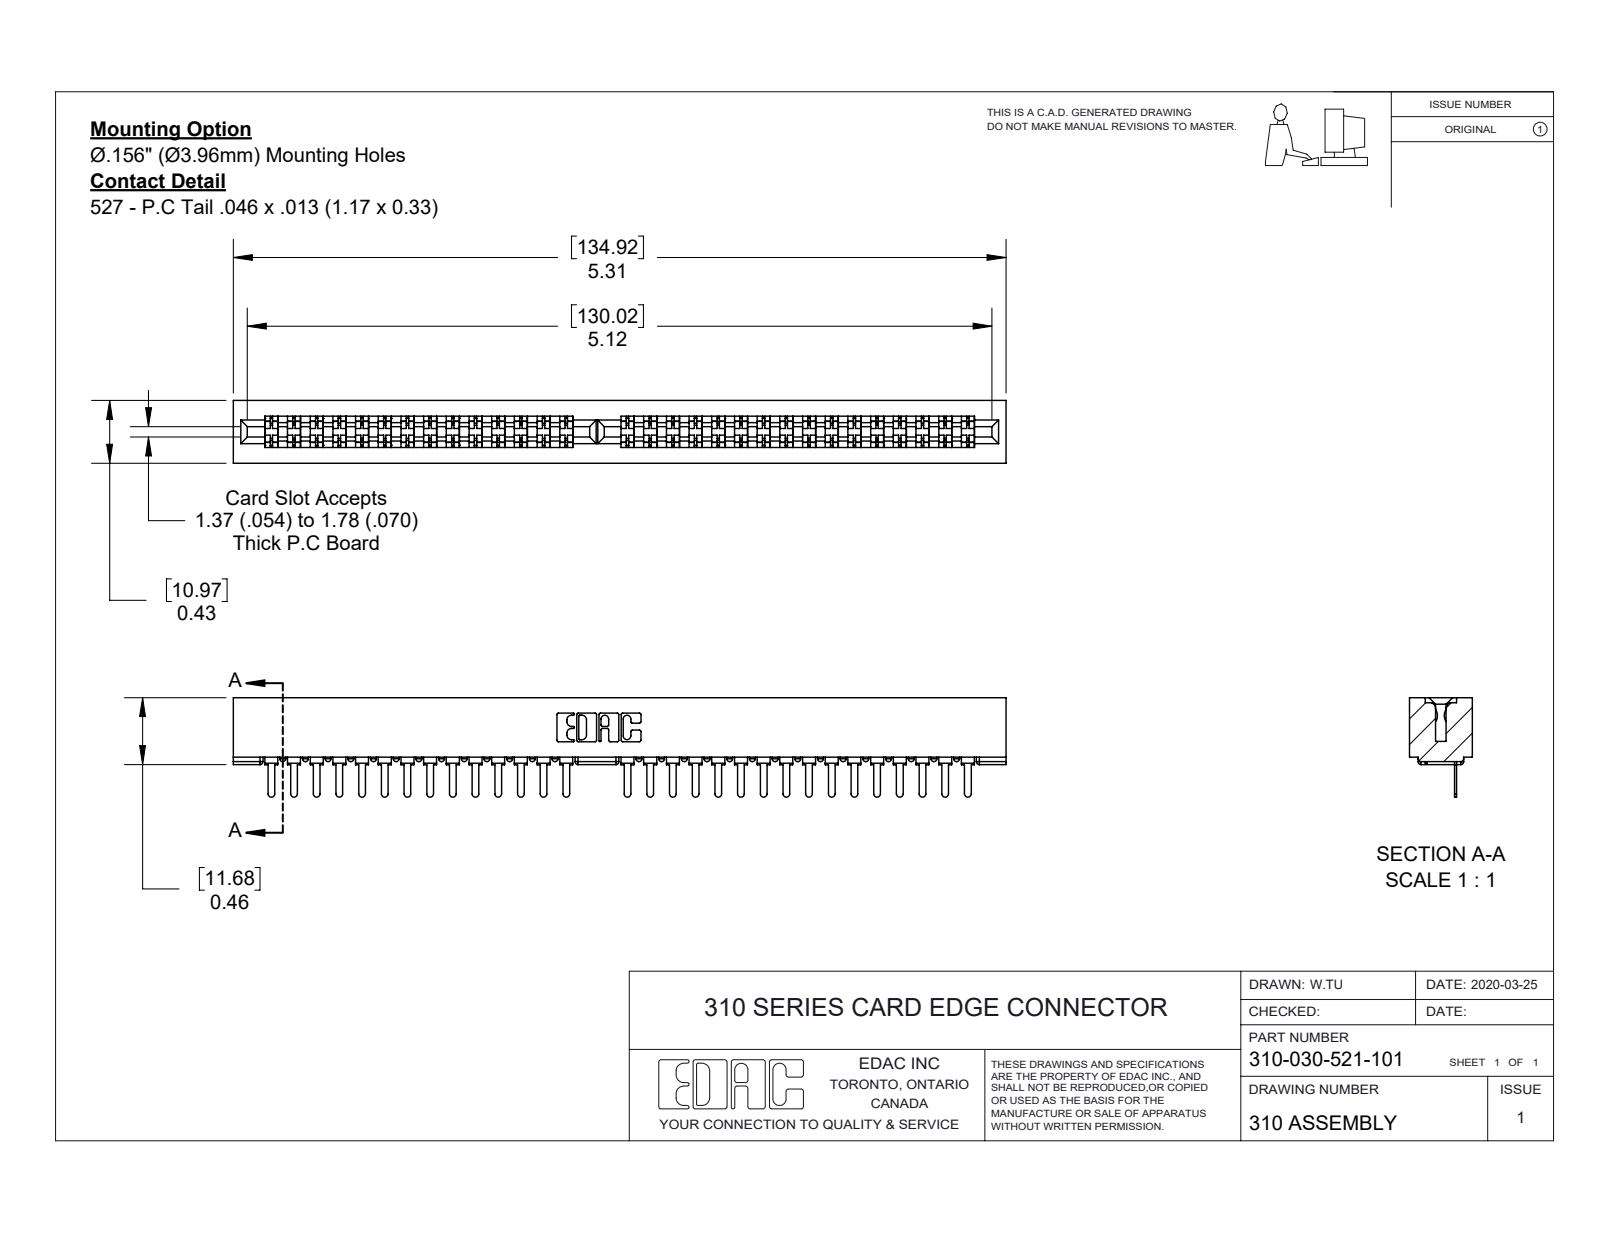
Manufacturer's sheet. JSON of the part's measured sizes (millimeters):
{"part_name": "310-030-521-101; 307-290-002_521; 310 Part_No Mounting Lugs", "step_written_by": "SolidWorks 2016 (CONFIG_CONTROL_DESIGN)", "units": "millimeters", "bodies": {"solids": 31, "faces": 2378, "planar": 1430, "cylindrical": 884, "other": 64}, "overall_size": [134.93, 17.37, 10.97], "volume_mm3": 12103, "surface_area_mm2": 17415, "partial_cylinders_radius": [[0.51, 98], [0.58, 30], [0.25, 22], [0.17, 6], [0.8, 6], [0.67, 3], [0.31, 2], [0.64, 2]], "face_to_face_distances": [2.76, 8.22, 0.33, 3.09, 7.89, 5.13, 5.46, 10.98, 1.24, 3.89]}
